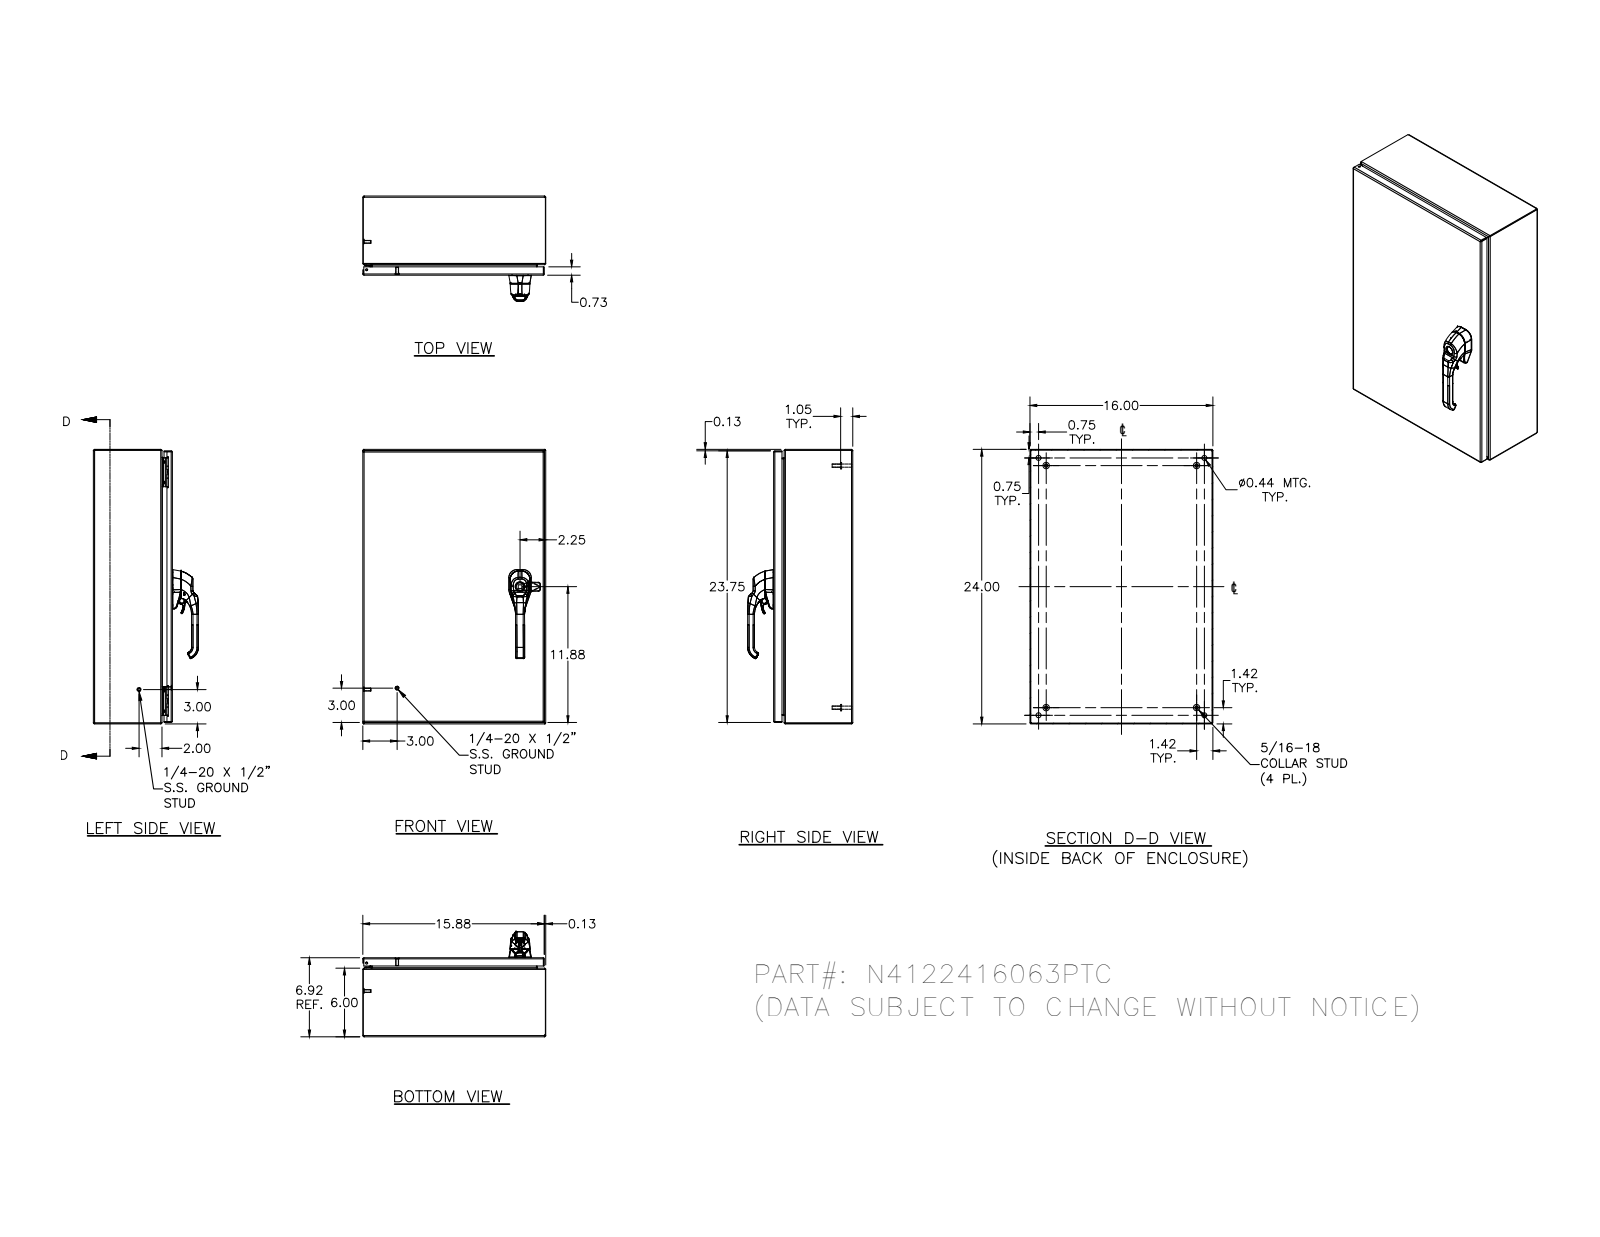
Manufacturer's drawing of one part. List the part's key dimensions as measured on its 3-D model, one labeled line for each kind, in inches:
Part name (STEP PRODUCT): N4122416063PTC
STEP written by: SolidWorks 2018 (AUTOMOTIVE_DESIGN)
Units: inches
Bodies: 29 solids, 1333 faces (433 planar, 495 cylindrical, 405 other)
Overall size (bounding box): 24 × 16 × 9.095
Volume: 114.1 in³ · Surface area: 2 876 in²
Round holes (diameter × count): ⌀0.188 ×5, ⌀0.093 ×4, ⌀0.152 ×4, ⌀0.167 ×4, ⌀0.172 ×4, ⌀0.437 ×4, ⌀0.156 ×2, ⌀0.187 ×1, ⌀0.413 ×1
Round bosses / shafts (diameter × count): ⌀0.25 ×10, ⌀0.563 ×4, ⌀0.36 ×4, ⌀0.32 ×4, ⌀0.3 ×4, ⌀0.275 ×4, ⌀0.256 ×4, ⌀0.164 ×4
Partial cylindrical surfaces — rounded edges, fillets, slot ends (radius × count): R0.031 ×30, R0.05 ×26, R0.105 ×20, R0.016 ×18, R0.125 ×14, R0.02 ×11, R0.032 ×8, R0.067 ×8
Main face-to-face distances: 0.074, 6.843, 6.917, 6.769, 15.926, 23.926, 15.852, 16, 5.926, 0.917
Hole centre spacings: 19.996, 0.017, 0.66, 20.656, 0.019, 0.5, 0.648, 0.656
